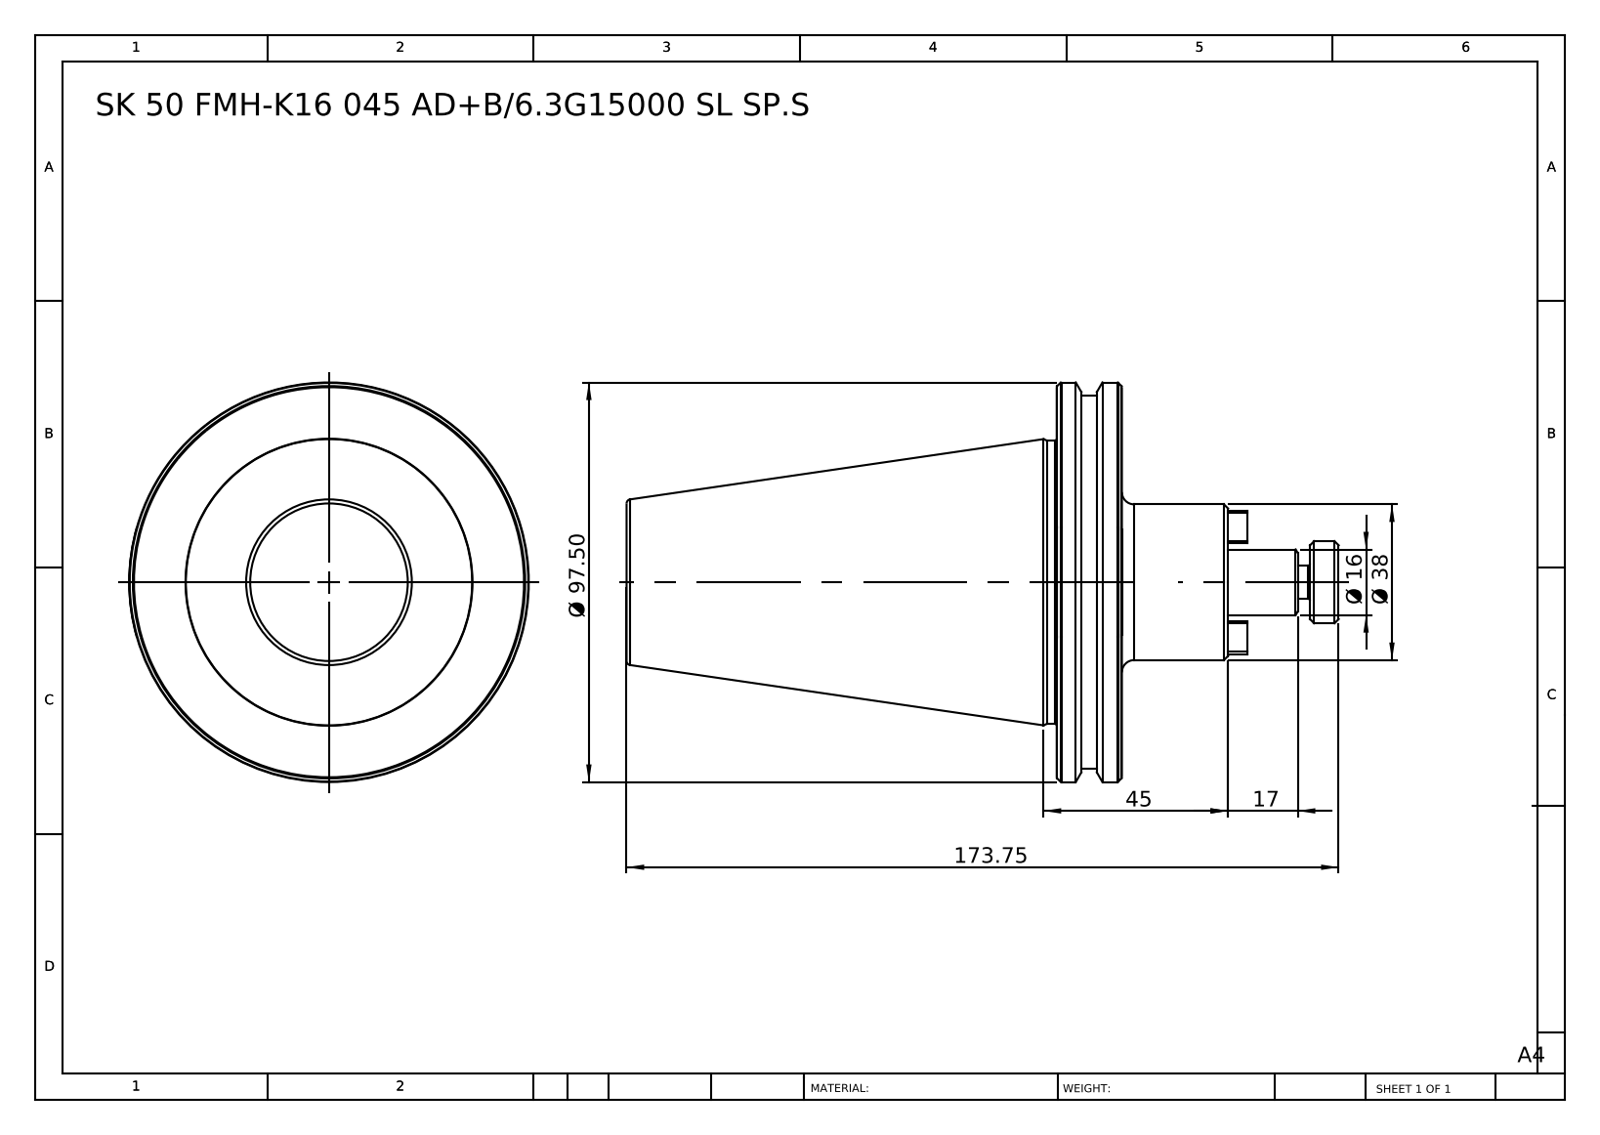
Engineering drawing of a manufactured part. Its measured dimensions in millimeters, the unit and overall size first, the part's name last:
Units: millimetres
Overall size (bounding box): 173.75 × 97.5 × 93.71
Round holes (diameter × count): ⌀10 ×1
Round bosses / shafts (diameter × count): ⌀91 ×1, ⌀69 ×1, ⌀38 ×1, ⌀20 ×1, ⌀16 ×1, ⌀8 ×1
Partial cylindrical surfaces — rounded edges, fillets, slot ends (radius × count): R0.8 ×4, R48.75 ×1
Main face-to-face distances: 15.9, 120.85, 104.95, 25.9, 41.8, 146.75, 27, 73.2, 52.9, 68.8
Volume: 399 925 mm³ · Surface area: 40 829 mm²
Bodies: 1 solid, 121 faces (52 planar, 25 cylindrical, 44 other)
Part name (STEP PRODUCT): SK40 FMH27 050 AD 6.3G15000 SL SP
STEP written by: SolidWorks 2014 (CONFIG_CONTROL_DESIGN)
